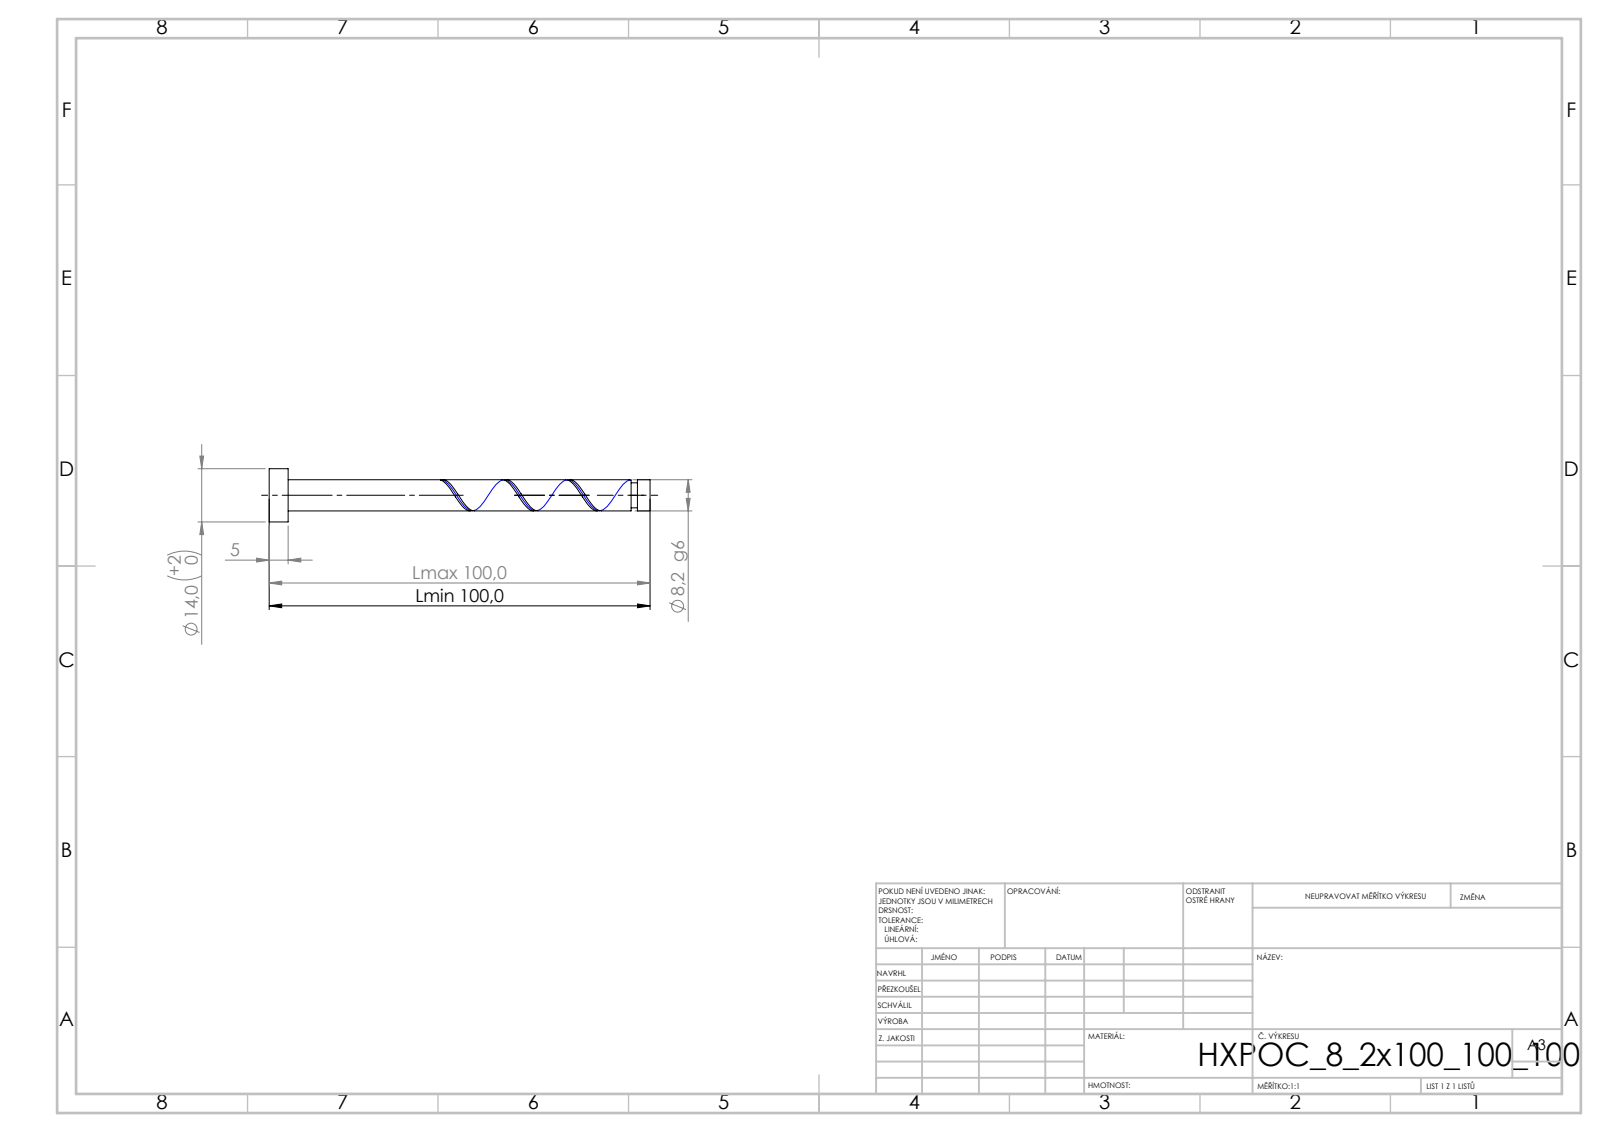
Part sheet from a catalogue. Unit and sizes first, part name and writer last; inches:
Units: inches
Overall size (bounding box): 3.937 × 0.551 × 0.551
Round bosses / shafts (diameter × count): ⌀0.551 ×1, ⌀0.323 ×1, ⌀0.258 ×1
Main face-to-face distances: 0.197, 3.937, 3.74, 3.806, 3.609, 0.131, 3.741, 3.544, 0.065, 0.196
Volume: 0.348 in³ · Surface area: 4.796 in²
Bodies: 1 solid, 21 faces (6 planar, 14 cylindrical, 1 other)
STEP written by: SolidWorks 2019 (CONFIG_CONTROL_DESIGN)
